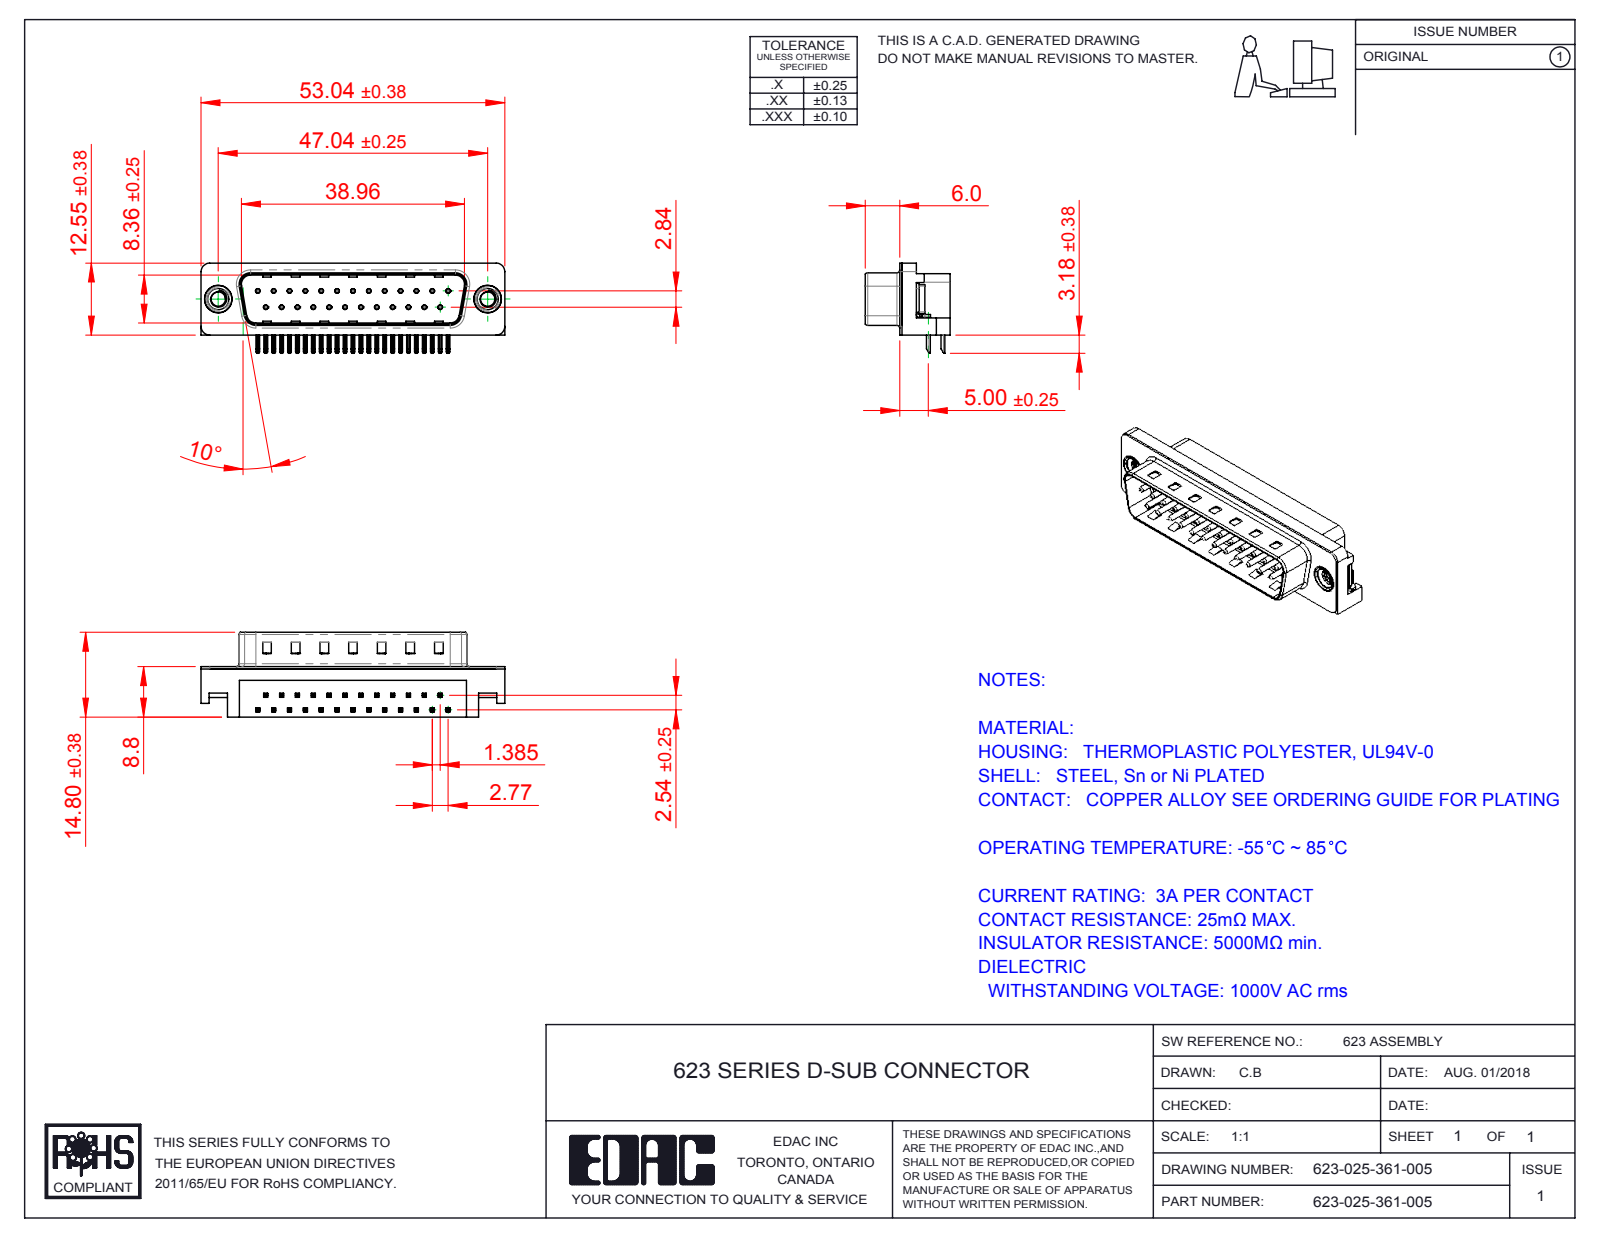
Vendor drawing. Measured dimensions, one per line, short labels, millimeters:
name: 623 Housing_25 Socket; 623 M3 Threaded Rivet; 623 Contact Top; 623-025-361-005 (+3 more)
written by: SolidWorks 2016 (CONFIG_CONTROL_DESIGN)
unit: mm
bodies: 31 solids, 2253 faces (1405 planar, 653 cylindrical, 195 other)
size: 53.04 × 15.73 × 14.8
volume: 4 719 mm³; area: 6 720 mm²
holes: 25× ⌀0.35, 25× ⌀0.8, 2× ⌀2.5, 2× ⌀4, 2× ⌀4.8, 2× ⌀5
bosses: 25× ⌀0.75, 2× ⌀4.9, 2× ⌀4.75, 2× ⌀3.9
rounds: 108× R0.25, 50× R0.12, 16× R1, 9× R0.5, 7× R1.5, 4× R0.9, 4× R1.6, 4× R2
face distances: 0.4, 8.4, 2.1, 1.7, 8.76, 10.46, 10.86, 10.35, 8.8, 5.9
hole spacings: 3.16, 2.77, 11.08, 5.54, 8.31, 5.03, 13.85, 7.48
